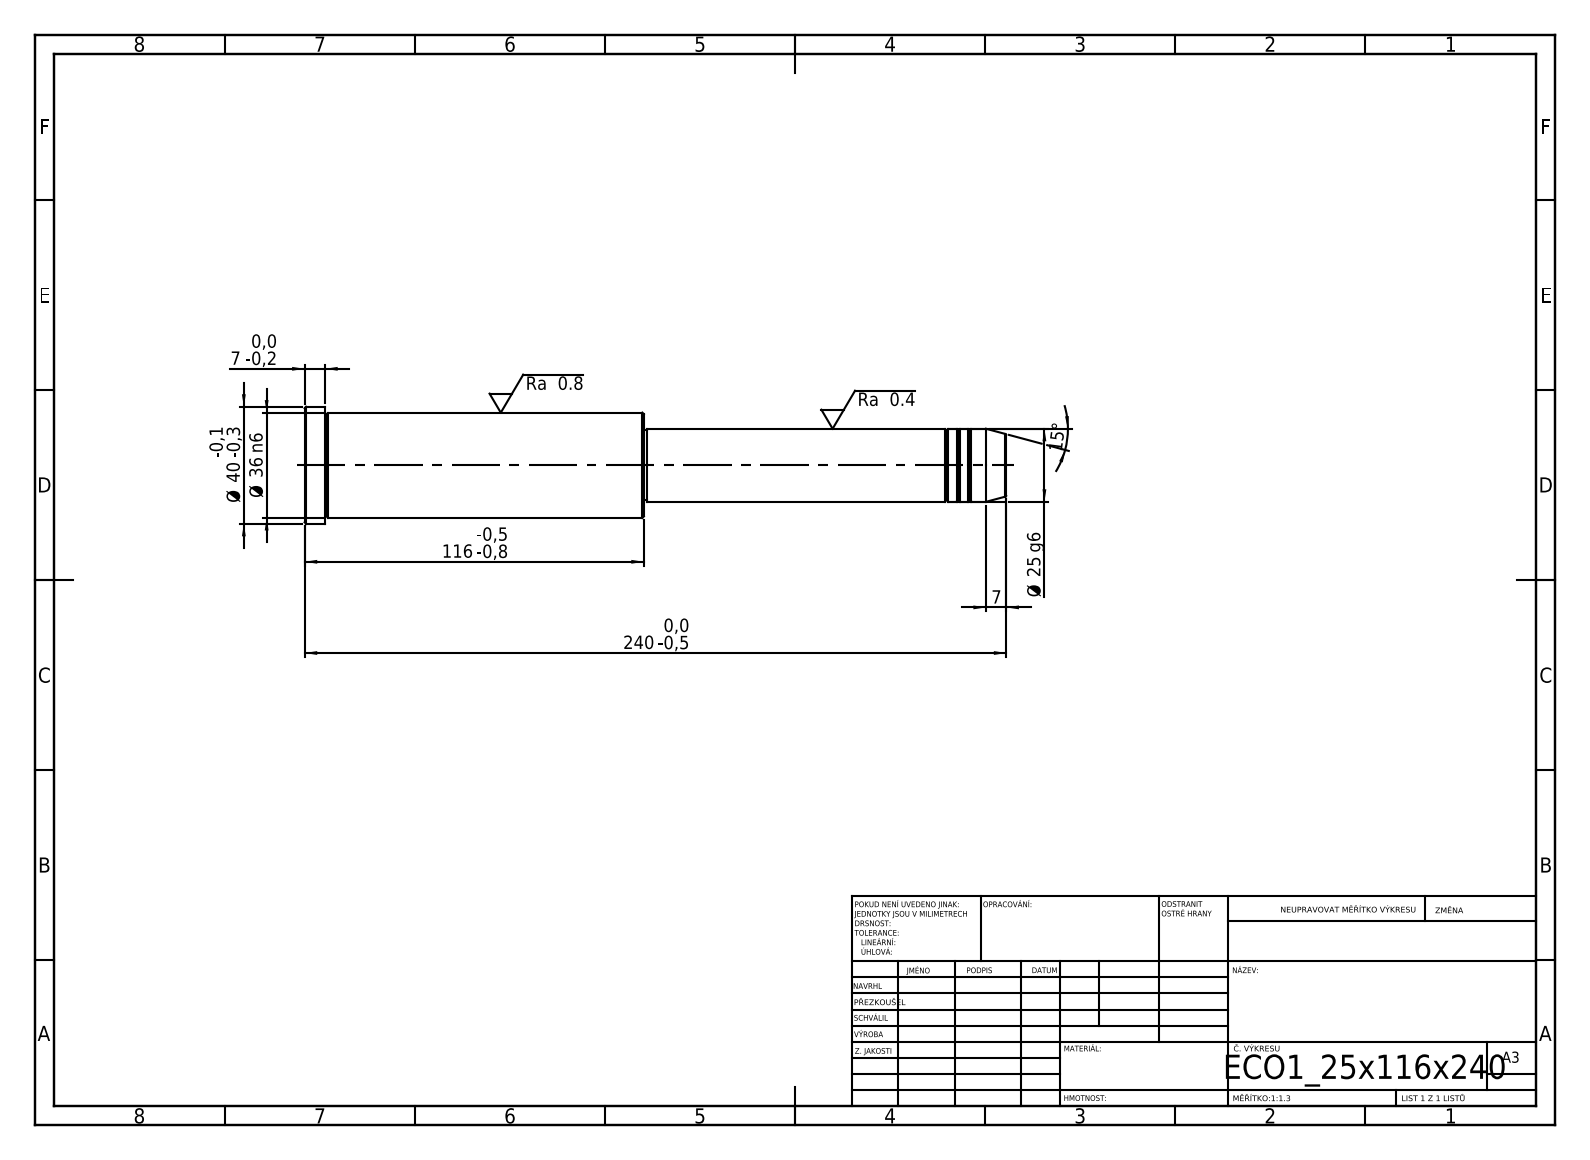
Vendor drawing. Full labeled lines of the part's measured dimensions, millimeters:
STEP written by: SolidWorks 2019 (CONFIG_CONTROL_DESIGN)
Units: millimetres
Bodies: 1 solid, 43 faces (5 planar, 14 cylindrical, 24 other)
Overall size (bounding box): 240 × 40 × 40
Volume: 179 919 mm³ · Surface area: 25 482 mm²
Round bosses / shafts (diameter × count): ⌀40 ×1, ⌀36 ×1, ⌀25 ×1, ⌀24 ×1
Main face-to-face distances: 116, 124, 240, 233, 109, 7, 123, 1, 110, 117
